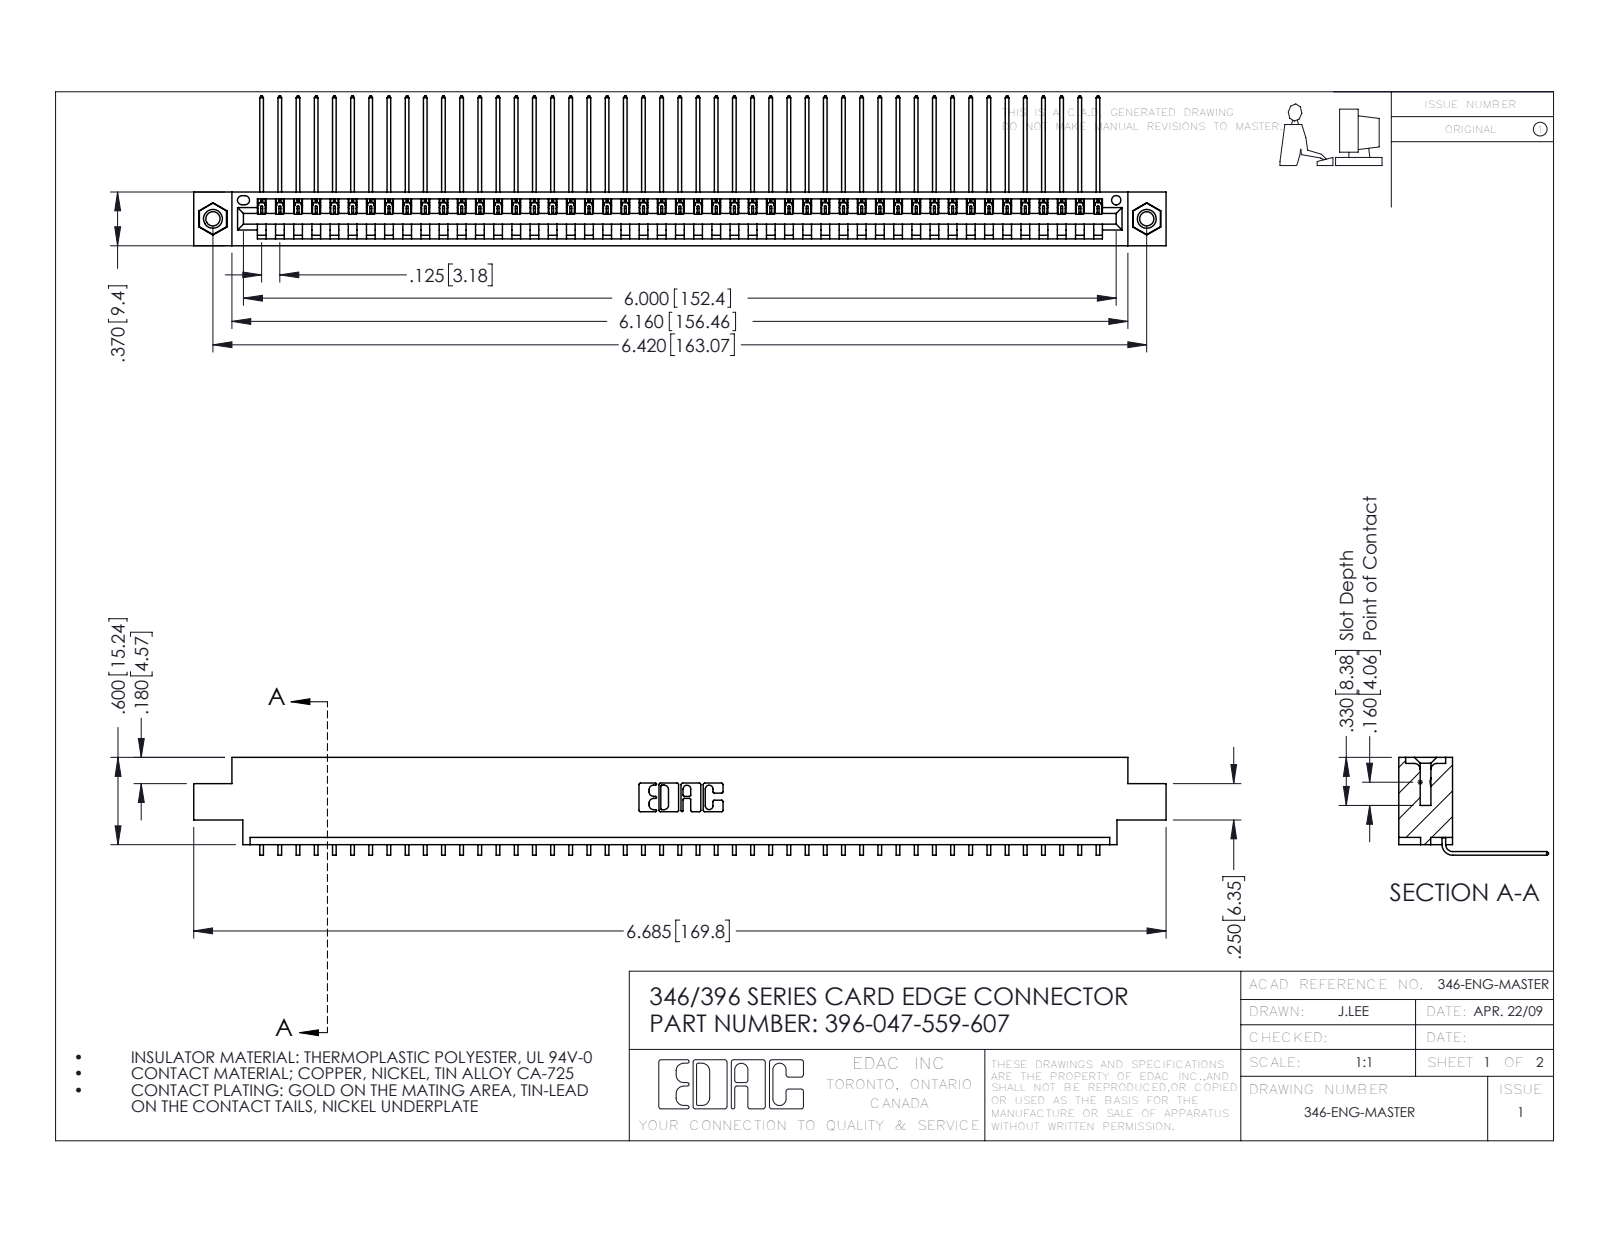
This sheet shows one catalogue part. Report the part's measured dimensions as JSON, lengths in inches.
{"part_name": "345-250-001_345-250-005-103; 346 Part_0.170 Offset - 0.156 Dia-TI; 396-047-559-607; 345-292-001_558 559 Tail - 1", "step_written_by": "SolidWorks 2016 (CONFIG_CONTROL_DESIGN)", "units": "inches", "bodies": {"solids": 50, "faces": 3006, "planar": 2086, "cylindrical": 904, "other": 16}, "overall_size": [6.685, 1.03, 0.673], "volume_in3": 0.993, "surface_area_in2": 33.37, "round_holes": [[0.098, 2], [0.125, 2], [0.156, 2], [0.064, 1]], "round_bosses_or_shafts": [[0.155, 2]], "partial_cylinders_radius": [[0.006, 94], [0.01, 22], [0.007, 6], [0.031, 6], [0.026, 3], [0.031, 2], [0.04, 2], [0.014, 1]], "face_to_face_distances": [0.048, 0.322, 0.37, 0.025, 0.25, 0.072, 0.222, 0.298, 0.148, 0.1], "hole_center_spacings": [0.246, 6.211, 6.42]}
